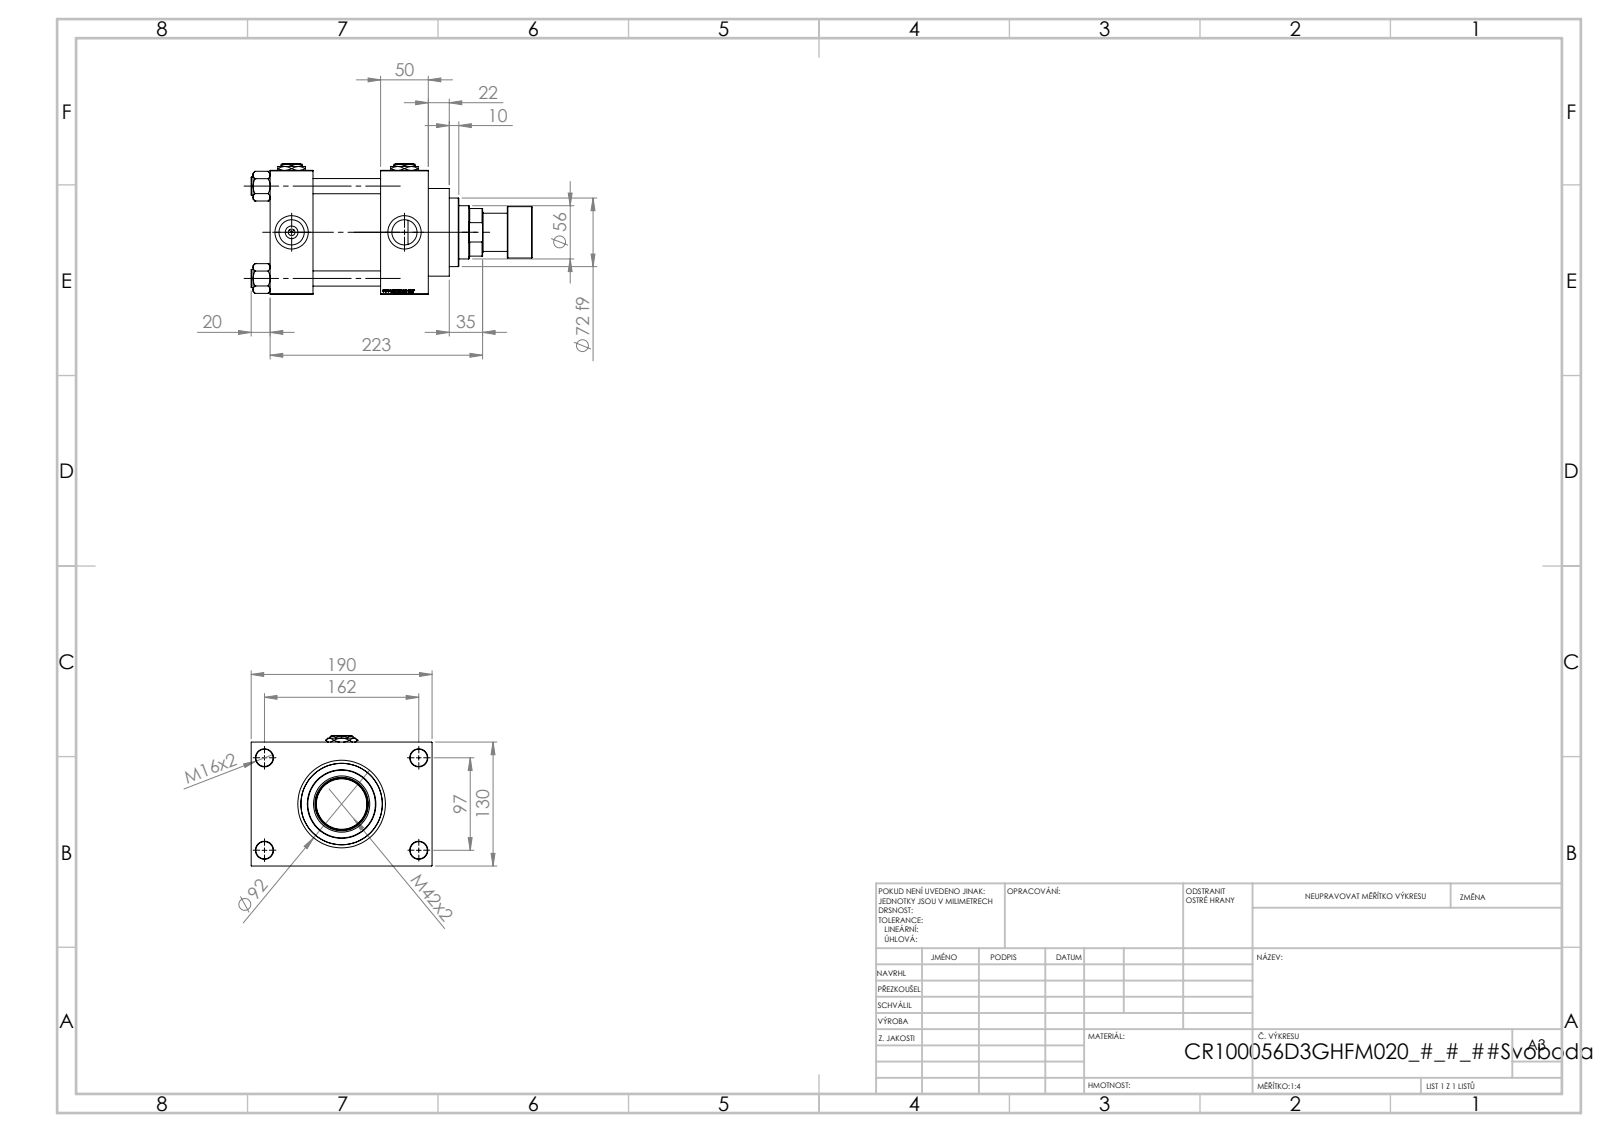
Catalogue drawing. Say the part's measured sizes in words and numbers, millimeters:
The part is named "V215CR_ROD_END_F; NUT_M5_D; Zatka_pro_OIL_PORT; V215CR_VCP_D (+3 more)". Its 3-D file was written by "SolidWorks 2019 (CONFIG_CONTROL_DESIGN)". It is 14 solids with 1266 faces: 597 planar, 103 cylindrical and 566 other. Overall it measures 295 by 190 by 137 millimeters. Its volume is 2 706 000 cubic millimeters and its surface area 381 823 square millimeters. Round holes: 4 of diameter 16, 4 of diameter 18, 4 of diameter 26.44, 4 of diameter 35, 3 of diameter 7, 1 of diameter 40.5, 1 of diameter 56, 1 of diameter 59, 1 of diameter 76, 1 of diameter 85.5, 1 of diameter 100. Round bosses or shafts: 4 of diameter 19, 1 of diameter 106, 1 of diameter 92, 1 of diameter 72, 1 of diameter 54, 1 of diameter 40. The main face-to-face distances are 130, 116, 50, 45, 71, 166, 121, 30, 160, 51. The hole center spacings are 32.55, 68.52, 94.41, 96.9, 102.27, 129.45, 161.73, 97.
